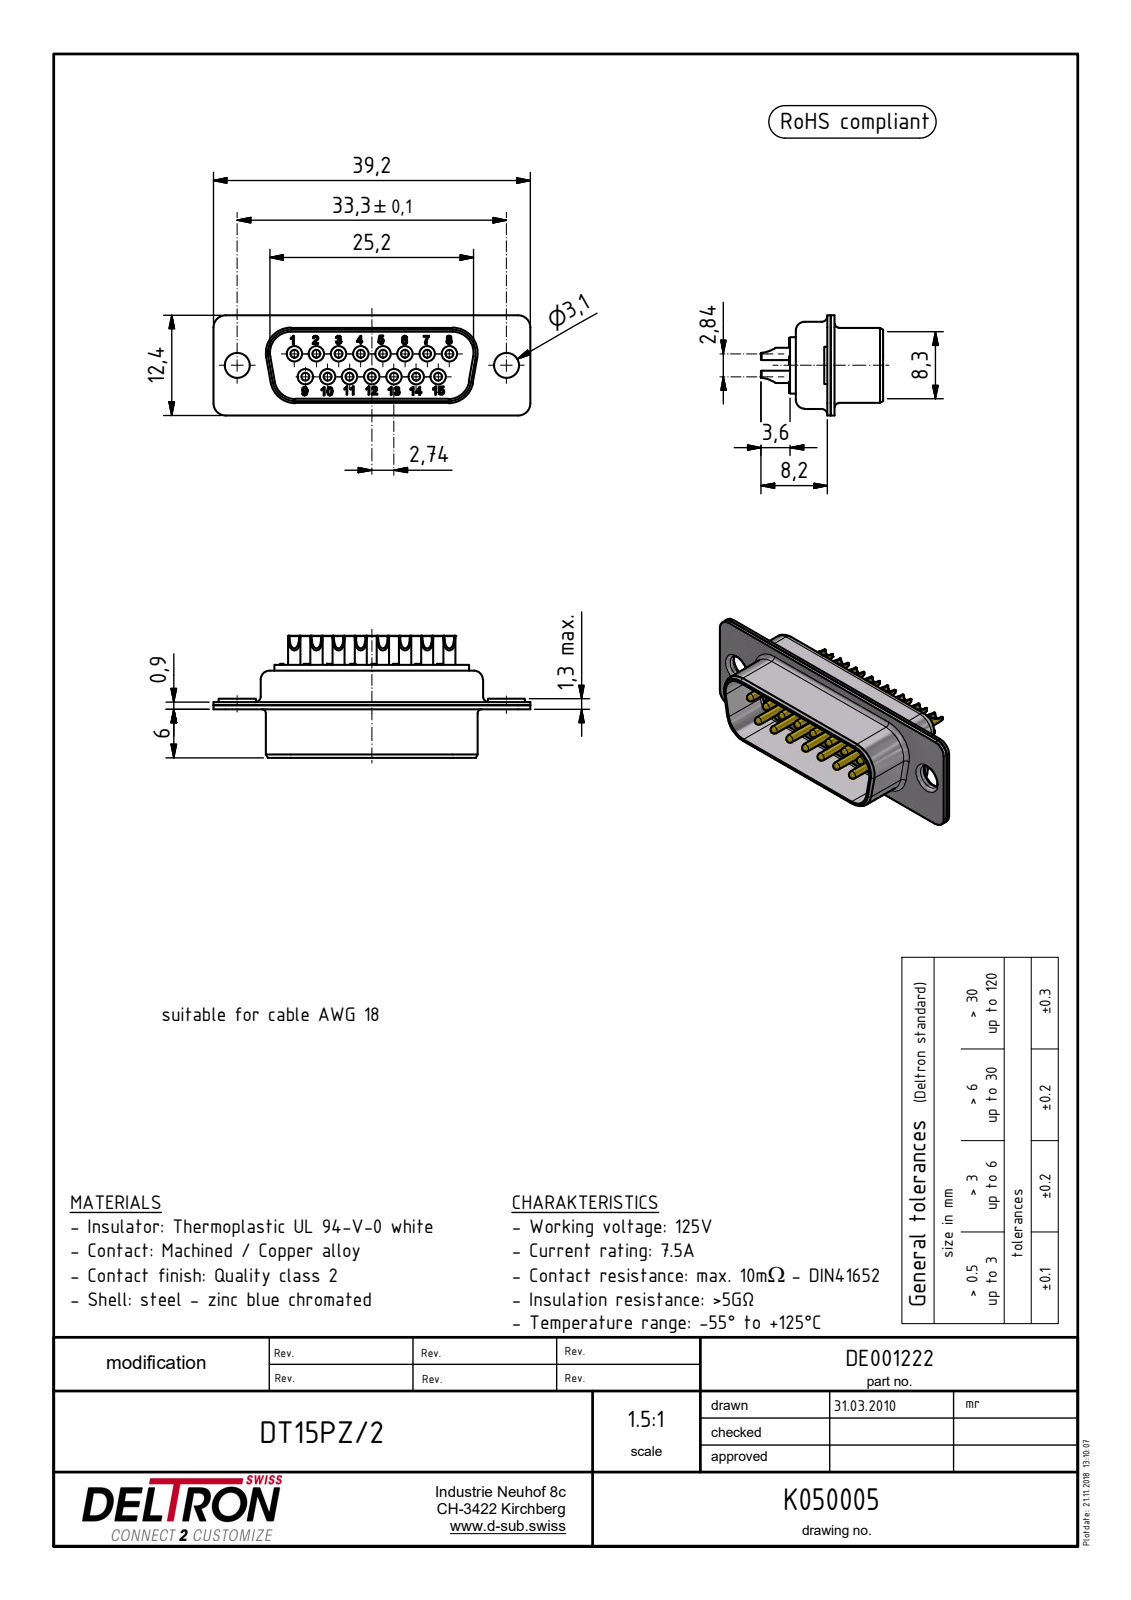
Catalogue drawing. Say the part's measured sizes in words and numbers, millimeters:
The part is named "N00403_BG; R+B00919_BG; R+B00153_BG; R+B00148_BG (+1 more)". Its 3-D file was written by "Autodesk Inventor 2015 (AUTOMOTIVE_DESIGN)". It is 18 solids with 1035 faces: 466 planar, 281 cylindrical and 288 other. Overall it measures 39.2 by 15.1 by 12.4 millimeters. Its volume is 1 653 cubic millimeters and its surface area 4 813 square millimeters. Round holes: 15 of diameter 1.2, 15 of diameter 1.92, 15 of diameter 2.3, 2 of diameter 0.34, 2 of diameter 3.1, 2 of diameter 4.06, 1 of diameter 0.24, 1 of diameter 0.28. Round bosses or shafts: 15 of diameter 2.23, 15 of diameter 1.96, 15 of diameter 1.94, 15 of diameter 1.6, 15 of diameter 1.6, 15 of diameter 1.5, 15 of diameter 1, 2 of diameter 4.6. Partial cylindrical surfaces (rounded edges, fillets, slot ends): 12 of radius 2, 8 of radius 0.25, 8 of radius 0.7, 8 of radius 1, 8 of radius 1.1, 4 of radius 0.5, 4 of radius 1.2, 4 of radius 1.5. The main face-to-face distances are 0.5, 0.4, 8.8, 0.65, 8.3, 0.8, 0.9, 0.6, 8.95, 9.45. The hole center spacings are 3.15, 2.74, 5, 5.48, 7.42, 8.22, 10, 10.96.
